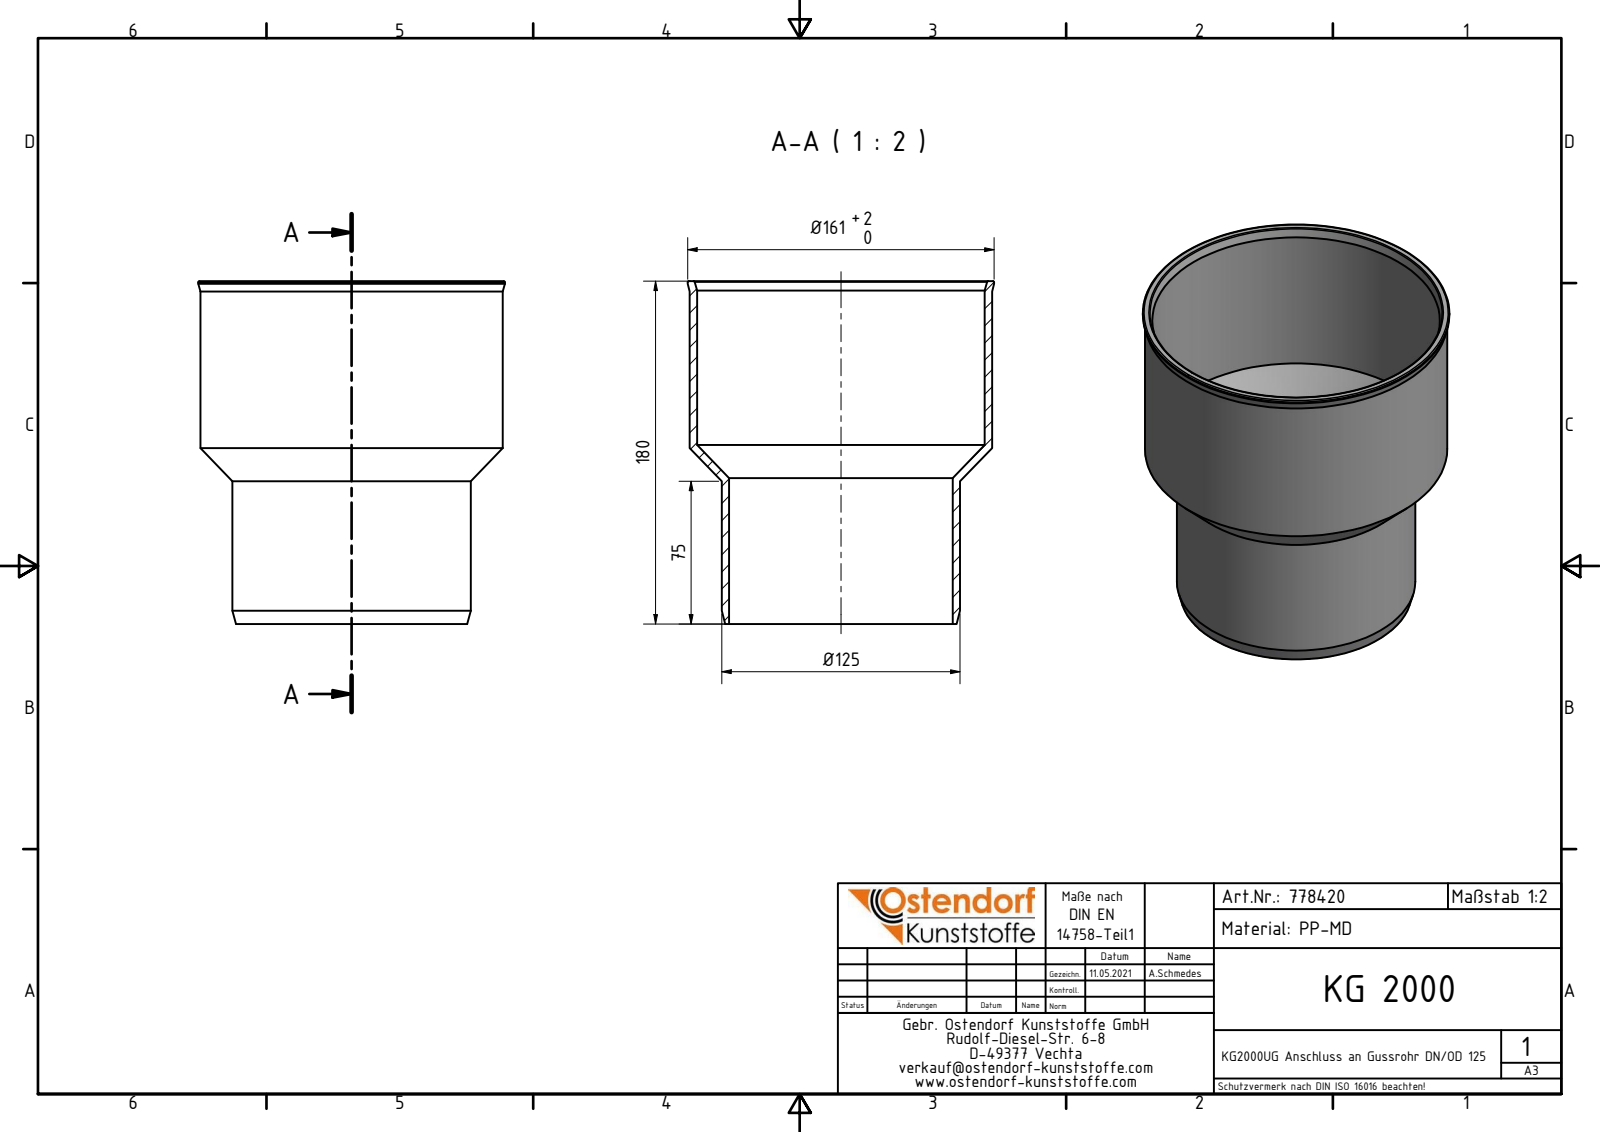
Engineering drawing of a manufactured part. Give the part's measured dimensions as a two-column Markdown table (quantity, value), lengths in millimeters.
| quantity | value |
| --- | --- |
| part name | 778420 KG2000UG Anschluss an Gussrohr DN_OD 125 |
| STEP written by | Autodesk Inventor 2020 (AUTOMOTIVE_DESIGN) |
| units | millimeters |
| bodies | 1 solid, 14 faces (2 planar, 5 cylindrical, 7 other) |
| overall size | 180 × 161 × 161 |
| volume | 315 997 mm³ |
| surface area | 165 861 mm² |
| round holes (diameter × count) | 117.4 × 1, 151 × 1 |
| round bosses / shafts (diameter × count) | 161 × 1, 158.8 × 1, 125.2 × 1 |
| main face-to-face distances | 180 |
